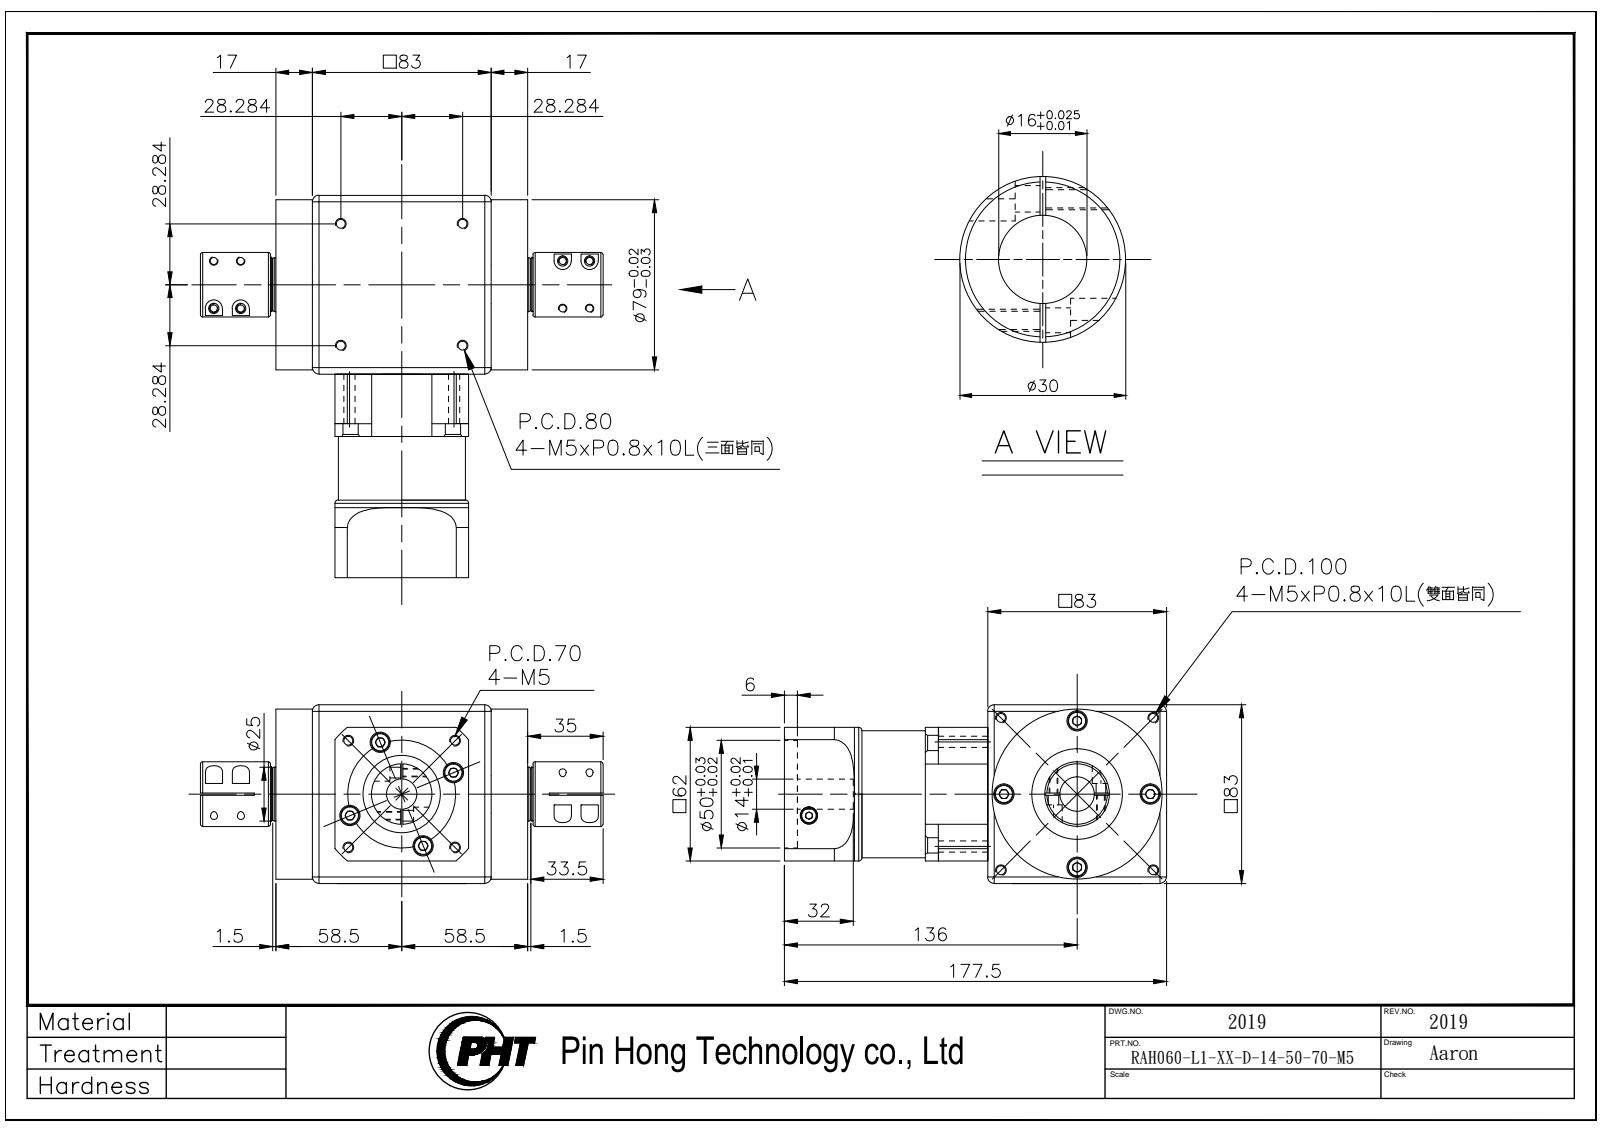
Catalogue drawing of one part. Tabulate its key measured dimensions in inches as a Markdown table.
| quantity | value |
| --- | --- |
| part name | RAH060-L1-XX-D-14-50-70-M5_2019 |
| STEP written by | SolidWorks 2016 (AUTOMOTIVE_DESIGN) |
| units | inches |
| bodies | 2 solids, 1006 faces (481 planar, 337 cylindrical, 188 other) |
| overall size | 7.362 × 6.988 × 3.268 |
| volume | 62.37 in³ |
| surface area | 193.2 in² |
| round holes (diameter × count) | 0.165 × 16, 0.161 × 8, 0.189 × 8, 0.205 × 8, 0.374 × 8, 0.217 × 4, 0.315 × 2, 0.551 × 1, 0.63 × 1, 0.654 × 1, 1.417 × 1 |
| round bosses / shafts (diameter × count) | 0.335 × 12, 0.299 × 8, 0.276 × 8, 0.157 × 8, 3.11 × 1, 2.433 × 1, 2.323 × 1, 2.165 × 1 |
| partial cylindrical surfaces (radius × count) | 0.157 × 8, 0.197 × 4, 0.984 × 1, 1.339 × 1, 1.575 × 1, 2.25 × 1 |
| main face-to-face distances | 3.268, 0.413, 2.854, 3.524, 1.083, 2.441, 0.669, 0.079, 4.606, 1.201 |
| hole center spacings | 2.093, 2.227, 0.196, 0.492, 0.583, 0.741, 0.866, 0.996 |
